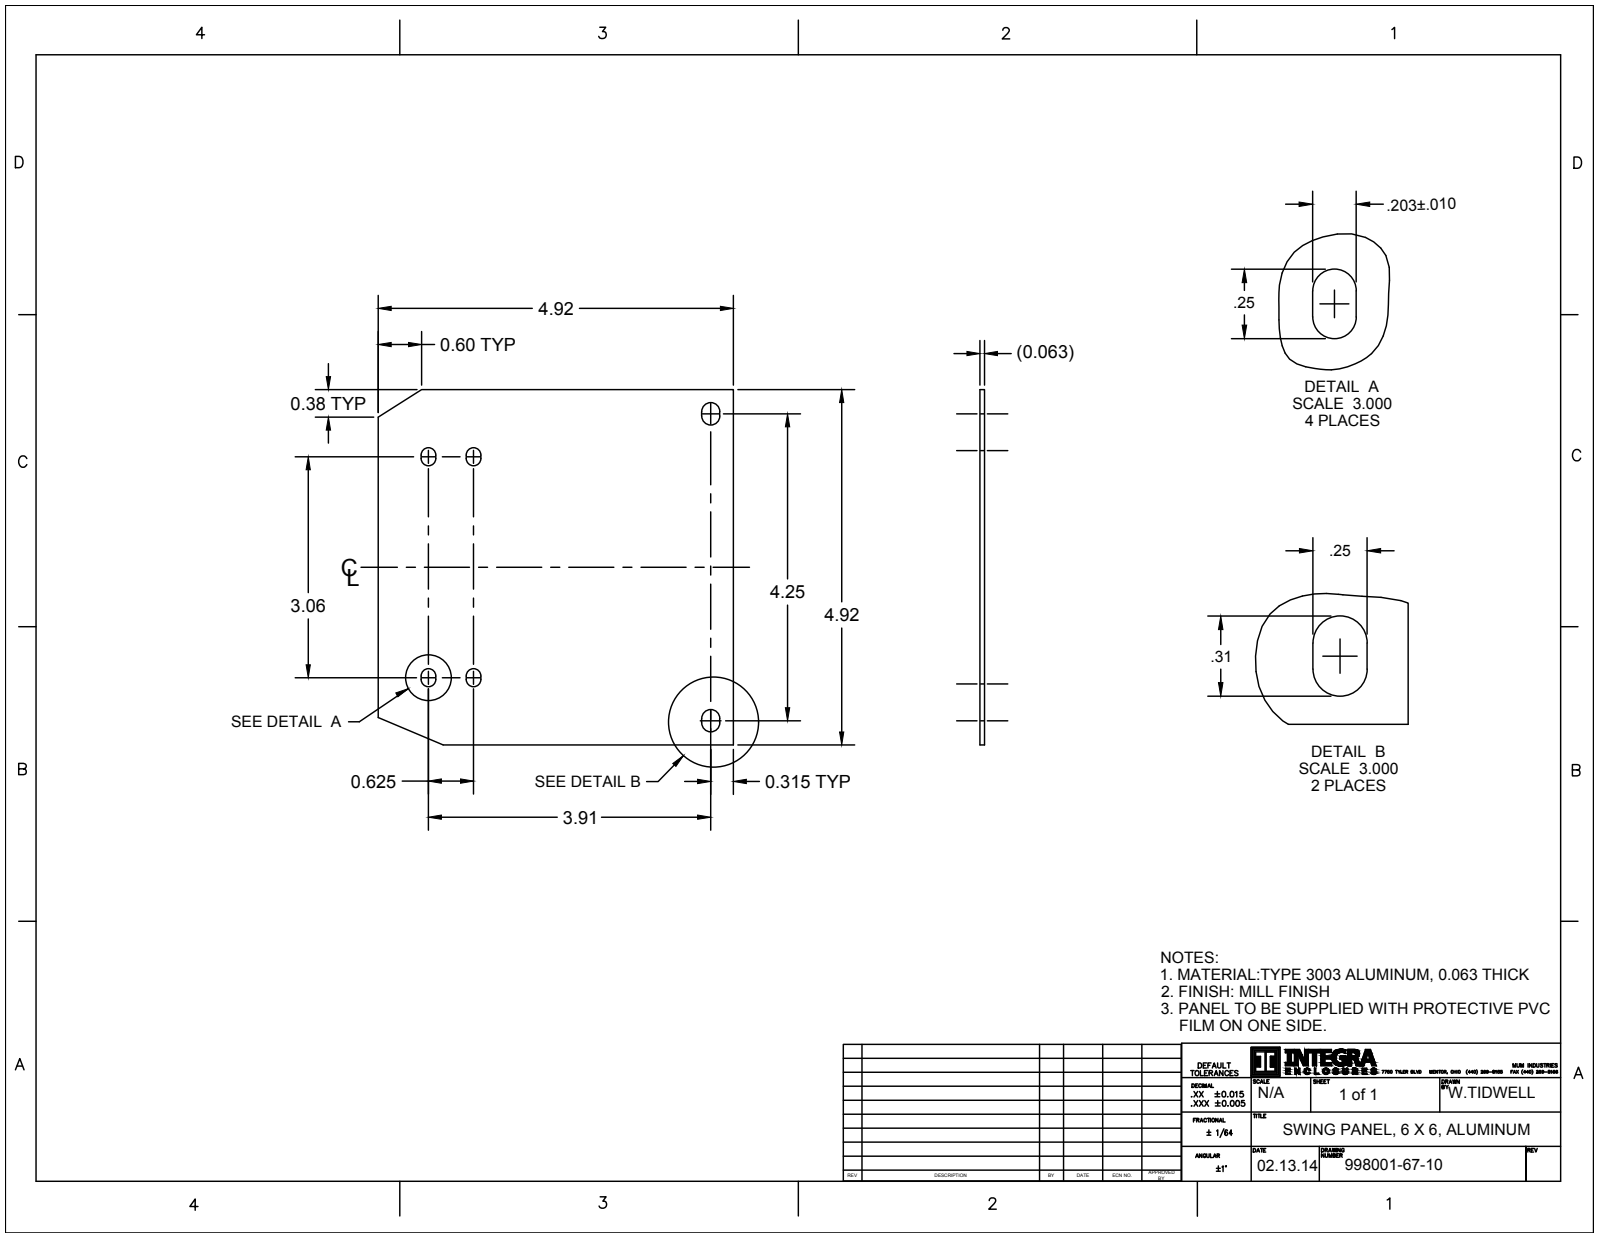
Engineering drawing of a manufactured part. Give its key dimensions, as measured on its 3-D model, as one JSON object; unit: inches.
{"part_name": "9912511-20-50; 9912525-80-10; 9912511-20-50_ASM; 995008-20-90 (+8 more)", "step_written_by": "CREO PARAMETRIC BY PTC INC, 2016050 (CONFIG_CONTROL_DESIGN)", "units": "inches", "bodies": {"solids": 31, "faces": 2116, "planar": 478, "cylindrical": 994, "other": 644}, "overall_size": [5.727, 5.727, 1.609], "volume_in3": 4.52, "surface_area_in2": 99.31, "round_holes": [[0.19, 8], [0.246, 8], [0.357, 8], [0.208, 4], [0.314, 4], [0.271, 2]], "round_bosses_or_shafts": [[0.25, 12], [0.3, 8], [0.298, 8], [0.29, 8], [0.26, 8], [0.258, 8], [0.44, 6], [0.43, 6]], "partial_cylinders_radius": [[0.03, 120], [0.004, 48], [0.005, 42], [0.05, 36], [0.029, 16], [0.046, 16], [0.06, 16], [0.02, 12]], "face_to_face_distances": [0.062, 3.08, 0.5, 0.11, 0.028, 3.58, 0.38, 0.11, 1.2, 2.58], "hole_center_spacings": [4.25, 0.11, 0.625, 0.677, 1.13, 3.08, 3.142, 3.335]}
